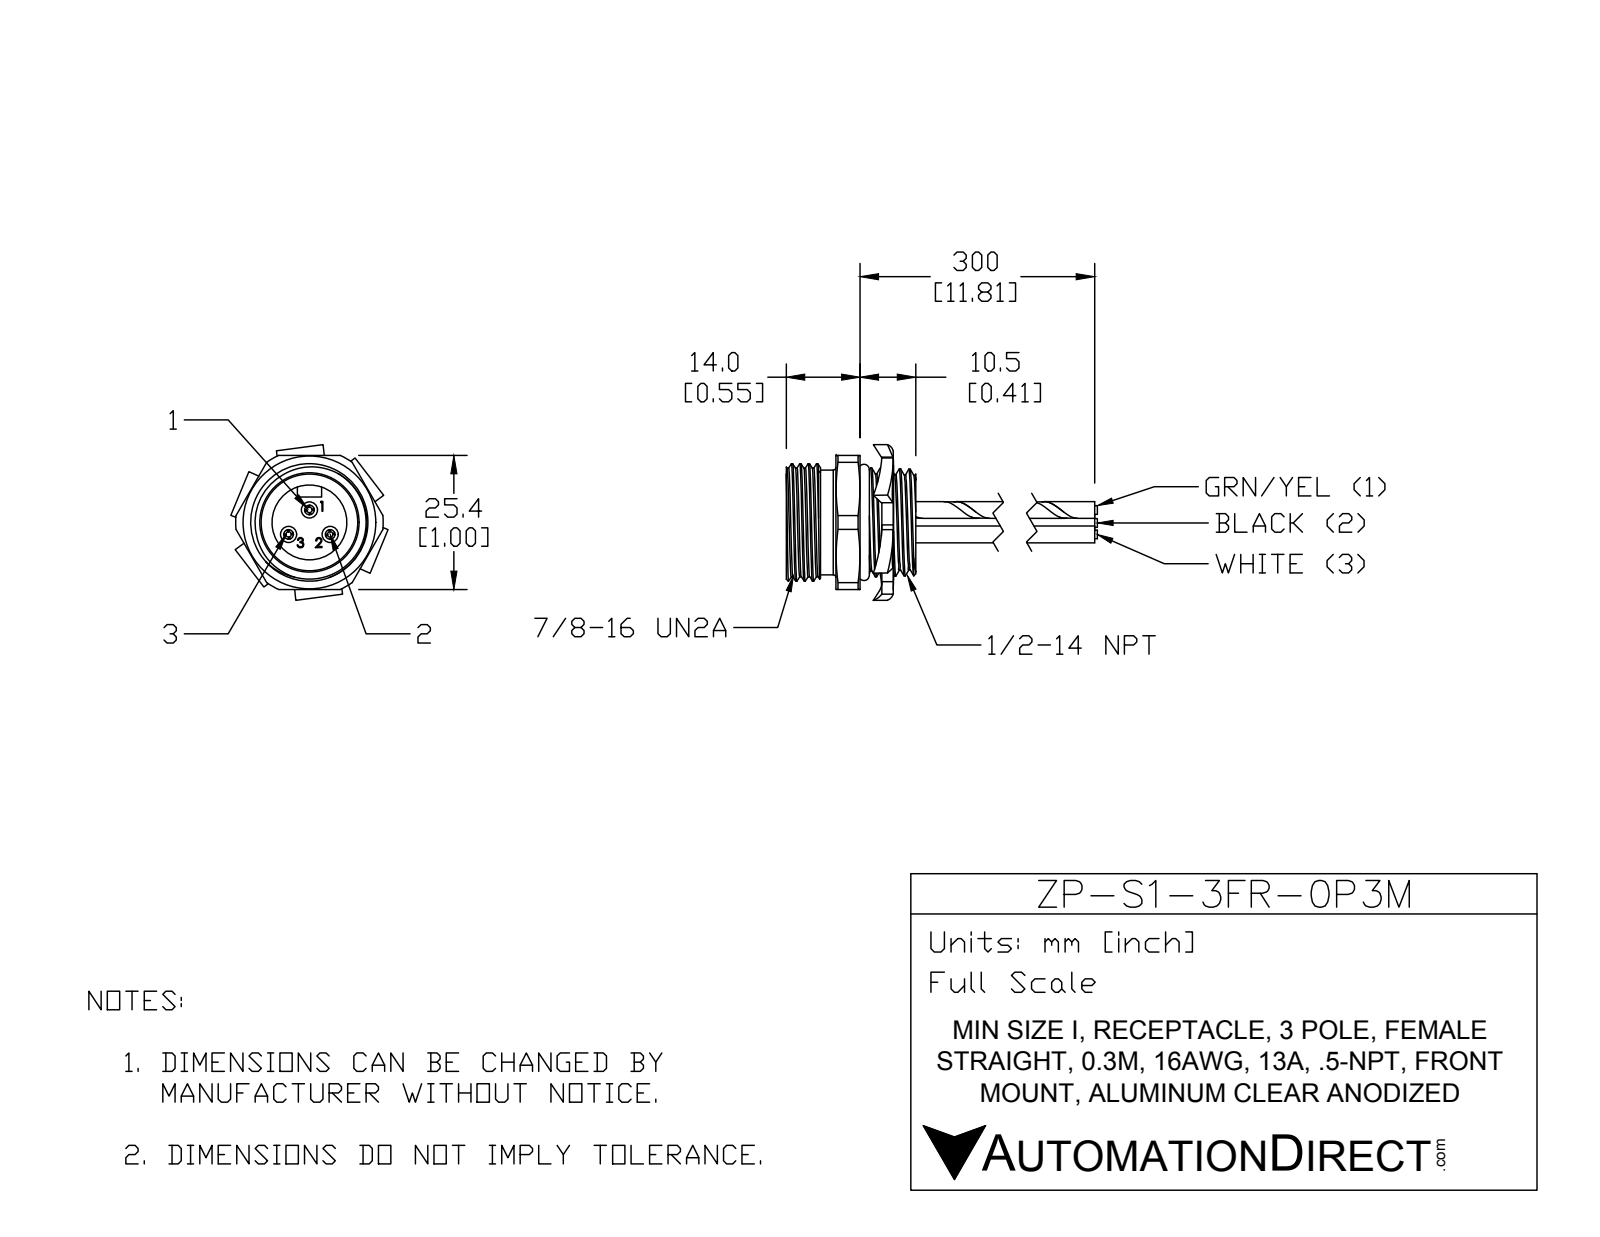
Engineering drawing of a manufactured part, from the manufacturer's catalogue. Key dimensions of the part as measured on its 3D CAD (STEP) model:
Part name (STEP PRODUCT): MIN-3FR-ZZ
STEP written by: SolidWorks 2015 (AUTOMOTIVE_DESIGN)
Units: millimetres
Bodies: 1 solid, 212 faces (69 planar, 66 cylindrical, 77 other)
Overall size (bounding box): 49.51 × 29.77 × 29.48
Volume: 8 946 mm³ · Surface area: 5 894 mm²
Round holes (diameter × count): ⌀3.05 ×3, ⌀18.29 ×1, ⌀19.61 ×1
Round bosses / shafts (diameter × count): ⌀3.18 ×3, ⌀25.37 ×1, ⌀22.22 ×1, ⌀20.6 ×1, ⌀19.93 ×1, ⌀19.81 ×1, ⌀18.19 ×1, ⌀14.15 ×1
Partial cylindrical surfaces — rounded edges, fillets, slot ends (radius × count): R13.97 ×1
Main face-to-face distances: 15.11, 25.4, 4.57, 10.54, 7.8, 12.37, 22.91, 6.99, 0.81, 5.38
Hole centre spacings: 4.54, 6.07, 2.36, 7.88
